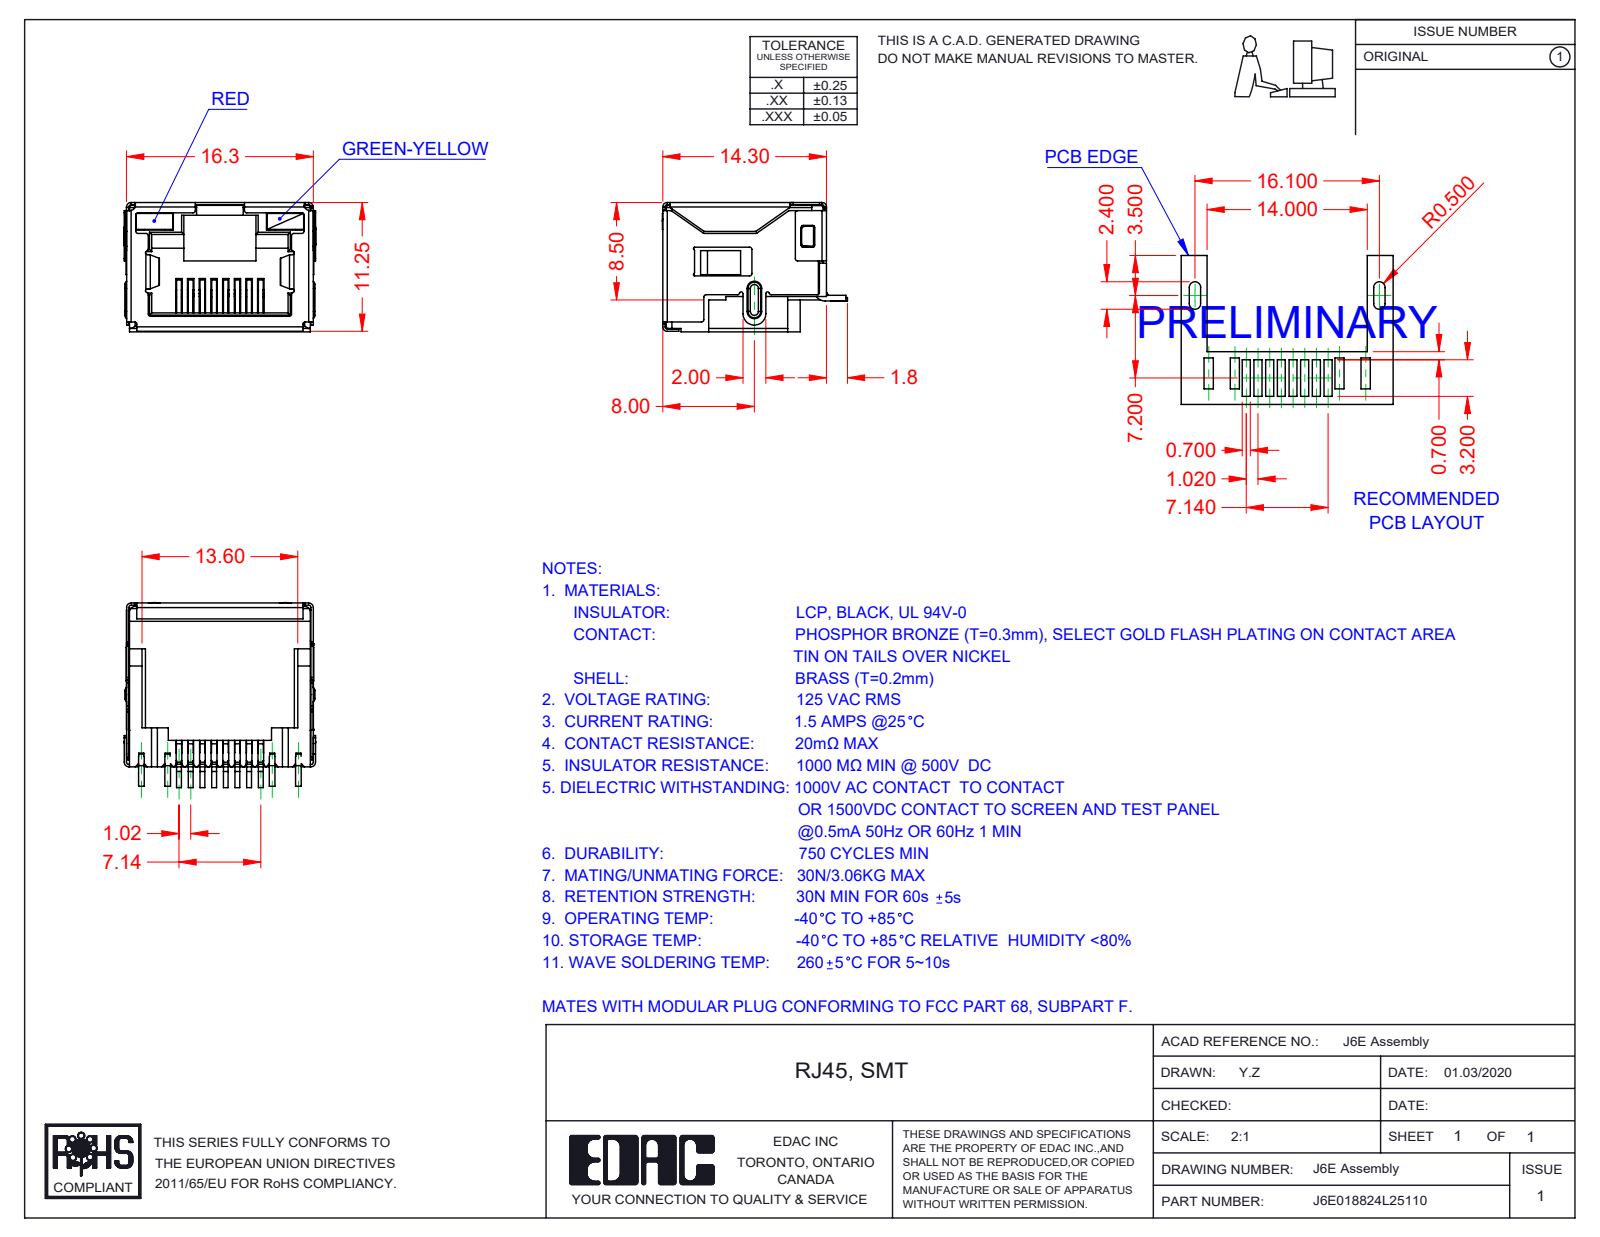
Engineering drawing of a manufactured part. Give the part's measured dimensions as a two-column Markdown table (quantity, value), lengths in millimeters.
| quantity | value |
| --- | --- |
| part name | 6E Shield_LED; 6E Insulator_LED; 6E LED RH_5-Green-Yellow; 6E LED LH_2-Red (+2 more) |
| STEP written by | SolidWorks 2016 (CONFIG_CONTROL_DESIGN) |
| units | millimeters |
| bodies | 12 solids, 1498 faces (1099 planar, 349 cylindrical, 50 other) |
| overall size | 16.75 × 16.15 × 11.3 |
| volume | 1 109 mm³ |
| surface area | 4 045 mm² |
| partial cylindrical surfaces (radius × count) | 0.2 × 82, 0.25 × 17, 0.4 × 13, 0.5 × 13, 0.1 × 10, 0.15 × 7, 0.3 × 4, 1 × 3 |
| main face-to-face distances | 11.05, 16.05, 16.1, 15.85, 11.1, 11.3, 2.4, 0.7, 9.85, 0.49 |
